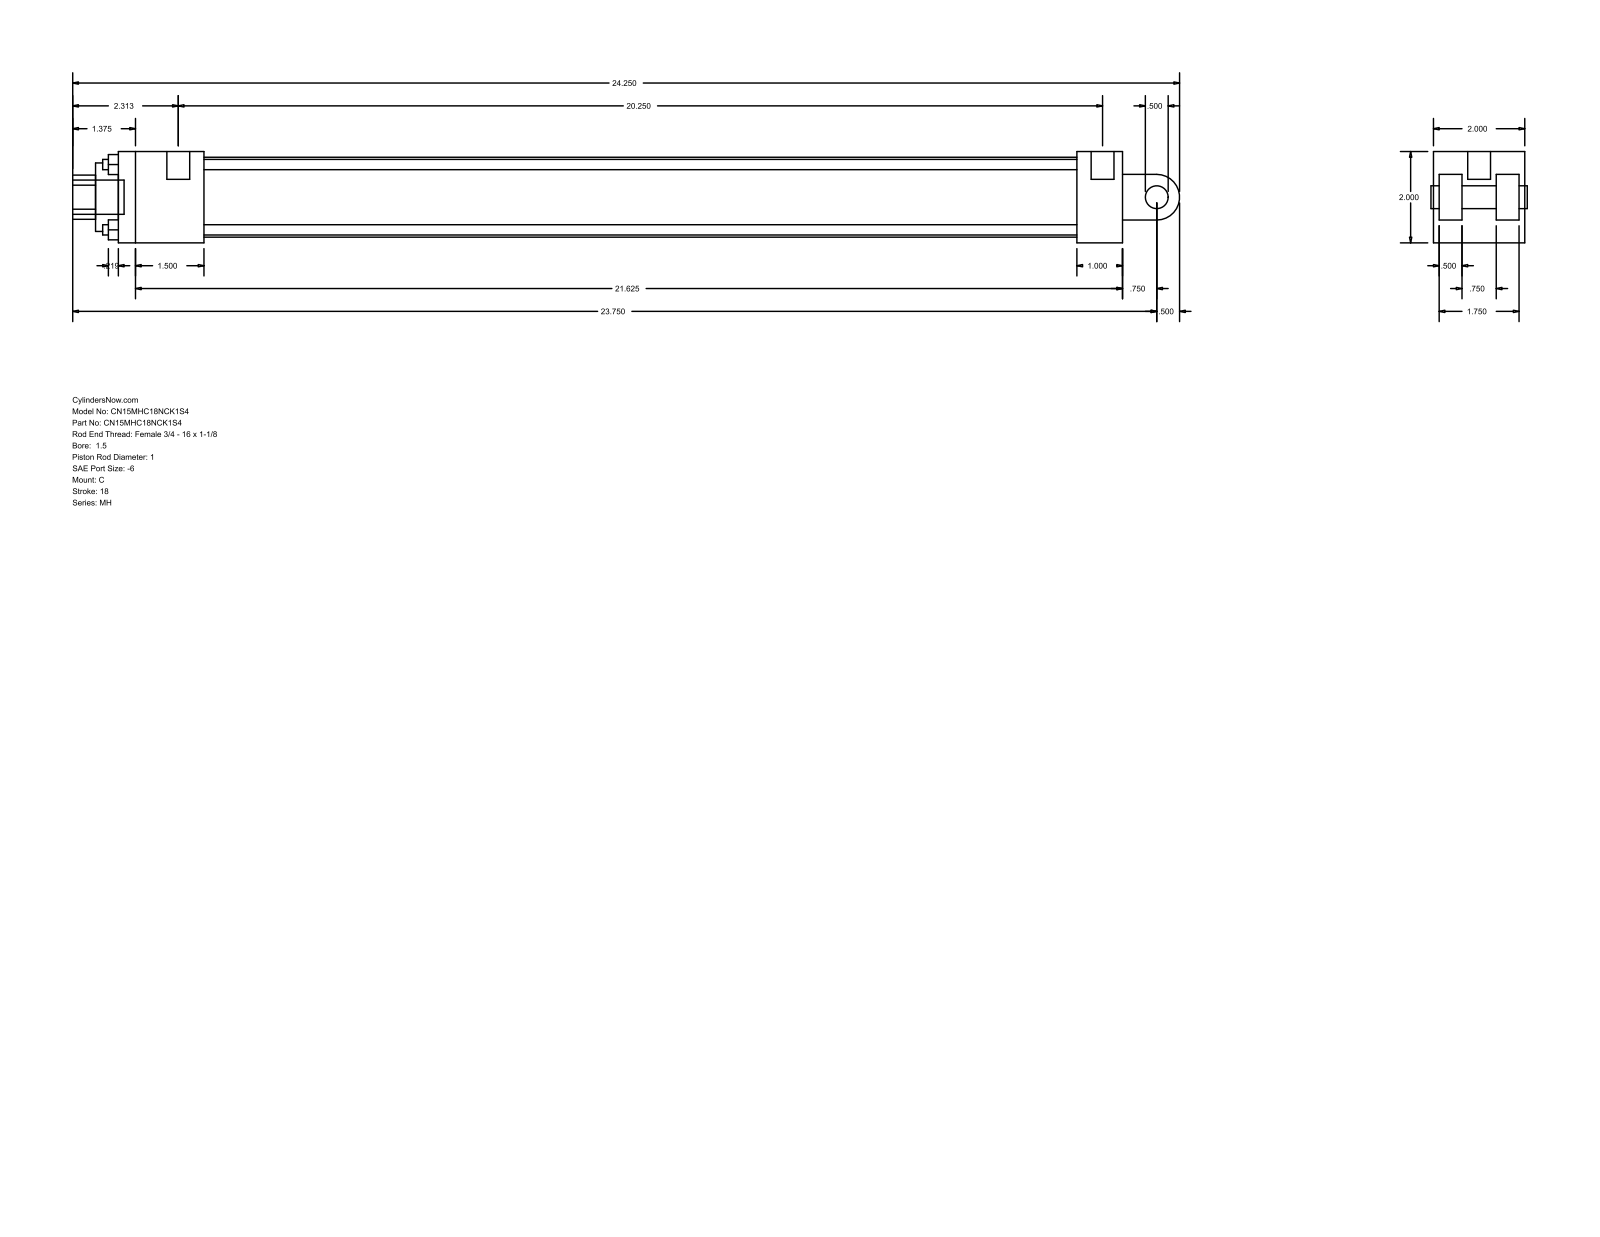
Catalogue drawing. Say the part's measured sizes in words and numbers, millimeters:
The part is named "MH_C__0150_1". Its 3-D file was written by "GSSL Pune (CONFIG_CONTROL_DESIGN)". It is 0 solids with 99 faces: 70 planar, 29 cylindrical and 0 other. Overall it measures 615.95 by 50.8 by 50.8 millimeters. Round holes: 4 of diameter 5.71, 2 of diameter 5.56, 1 of diameter 12.7, 1 of diameter 25.4, 1 of diameter 38.1, 1 of diameter 44.45. Round bosses or shafts: 2 of diameter 12.7, 2 of diameter 5.56, 1 of diameter 19.05. Partial cylindrical surfaces (rounded edges, fillets, slot ends): 1 of radius 12.29, 1 of radius 12.7. The main face-to-face distances are 50.8, 12.7, 47.63, 3.17, 15.87, 25.4, 34.93, 31.76, 558.8, 38.1. The hole center spacings are 25.68, 36.32, 51.36.
